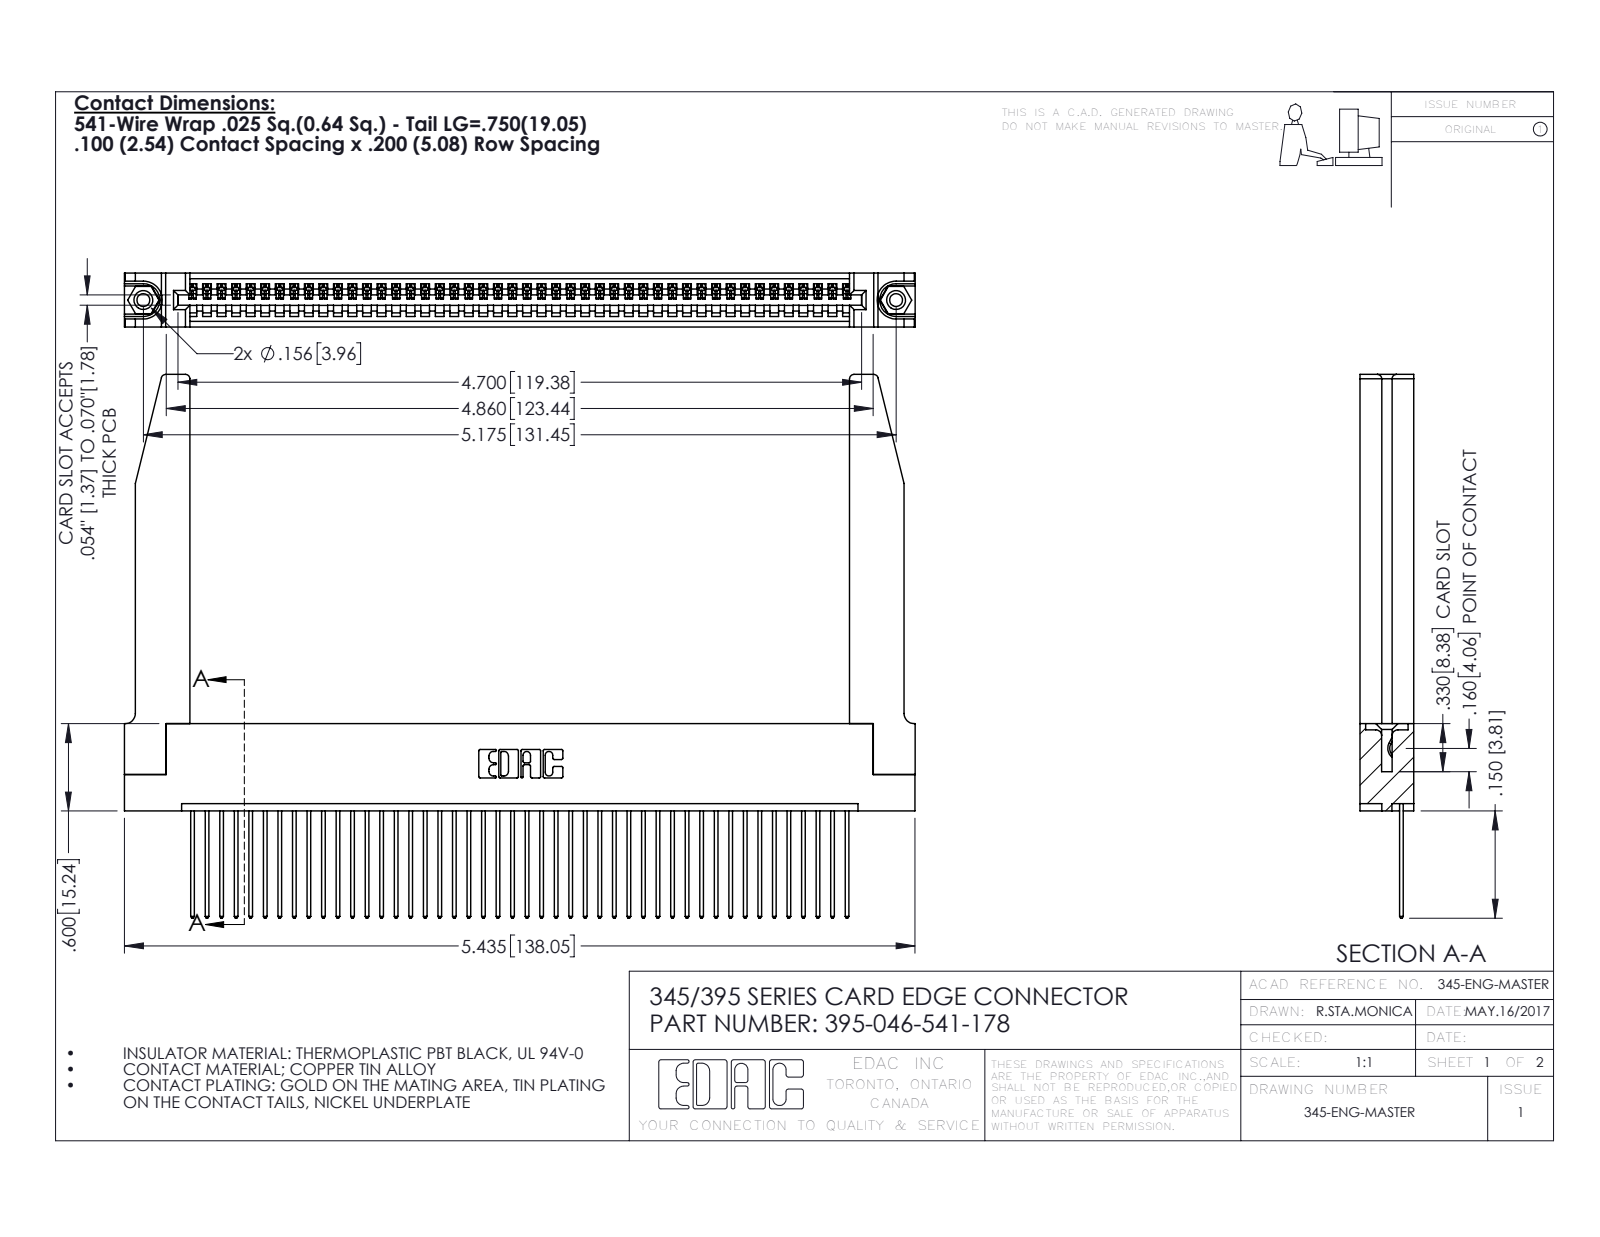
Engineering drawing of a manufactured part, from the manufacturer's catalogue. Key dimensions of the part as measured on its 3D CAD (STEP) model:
Part name (STEP PRODUCT): 345-220-078_345-220-078; 345 Part_Flush Mounting Lugs - 0.156 Dia-TH; 345-250-001_345-250-001-102; 345-292-001_345-293-141 (+1 more)
STEP written by: SolidWorks 2016 (CONFIG_CONTROL_DESIGN)
Units: inches
Bodies: 51 solids, 3028 faces (2062 planar, 914 cylindrical, 52 other)
Overall size (bounding box): 5.436 × 3.737 × 0.37
Volume: 1.286 in³ · Surface area: 39.47 in²
Round holes (diameter × count): ⌀0.089 ×2, ⌀0.125 ×2, ⌀0.156 ×2, ⌀0.064 ×1
Round bosses / shafts (diameter × count): ⌀0.155 ×2
Partial cylindrical surfaces — rounded edges, fillets, slot ends (radius × count): R0.006 ×92, R0.01 ×92, R0.01 ×22, R0.03 ×8, R0.007 ×6, R0.031 ×6, R0.026 ×3, R0.031 ×2
Main face-to-face distances: 0.072, 0.37, 0.298, 0.098, 0.272, 0.025, 0.2, 0.225, 0.148, 0.15
Hole centre spacings: 0.27, 4.939, 5.175
